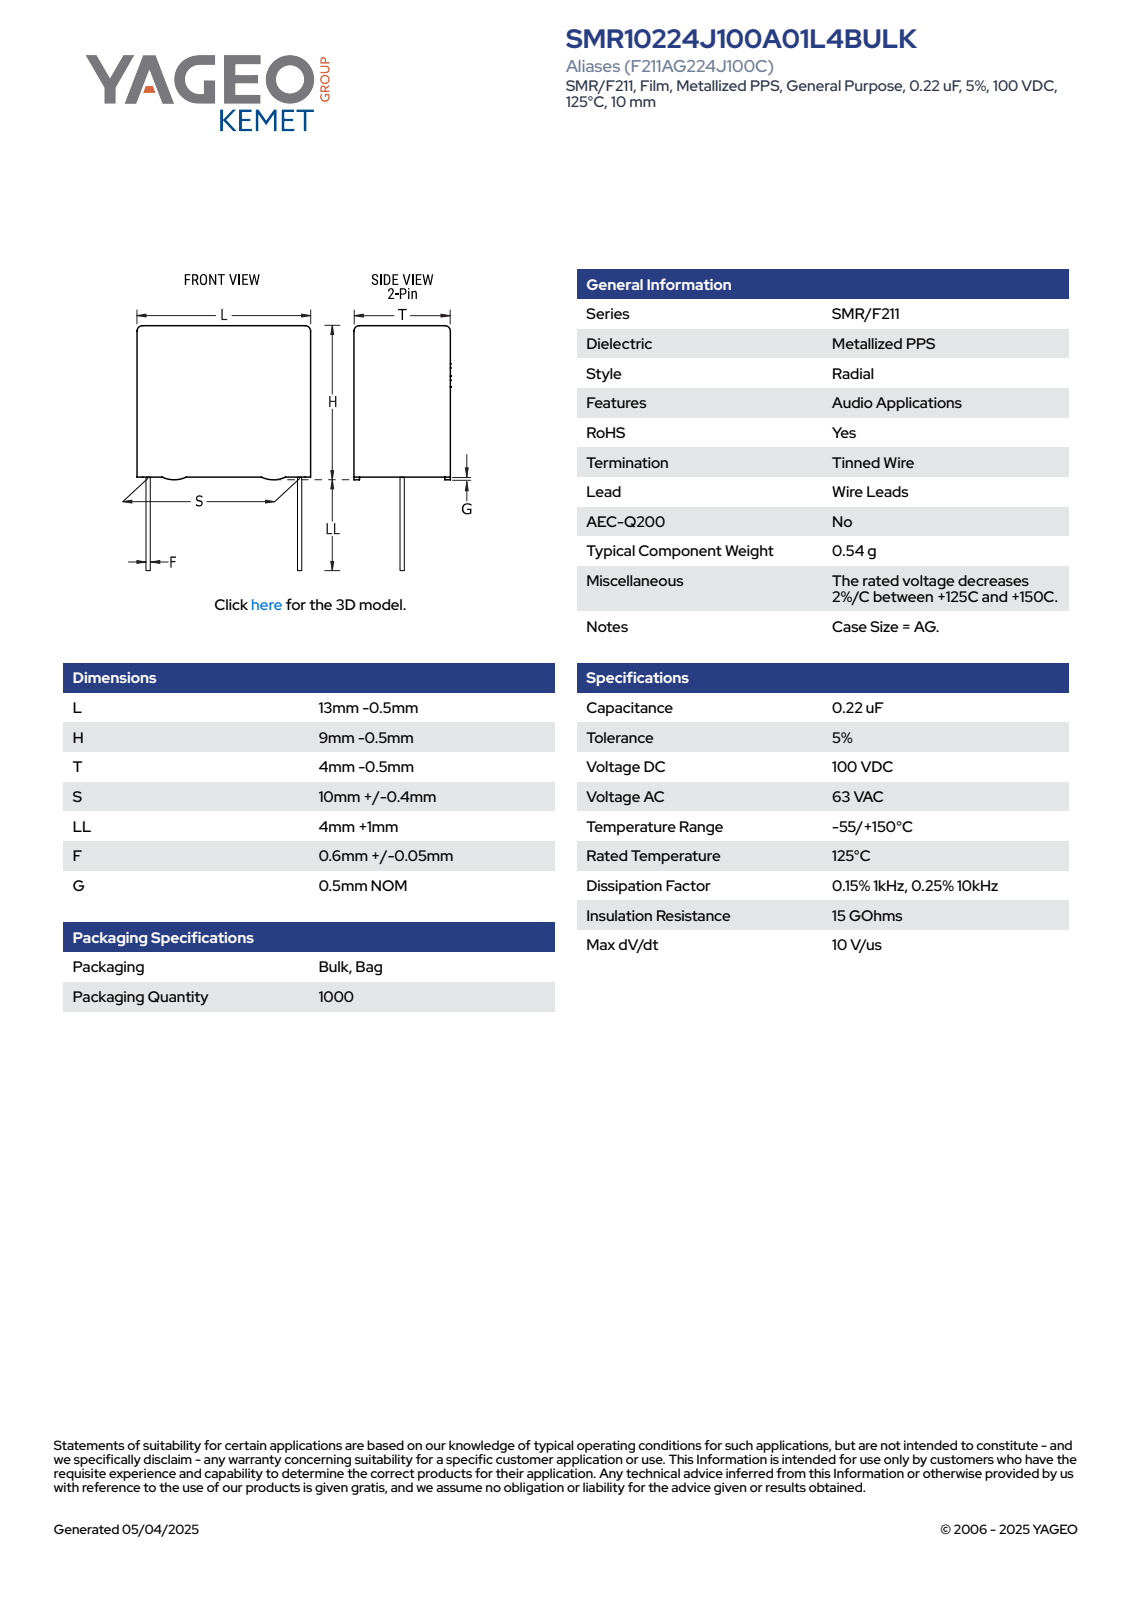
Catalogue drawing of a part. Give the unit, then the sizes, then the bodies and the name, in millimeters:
Units: millimetres
Overall size (bounding box): 13.5 × 12.5 × 3.5
Round bosses / shafts (diameter × count): ⌀0.65 ×2
Partial cylindrical surfaces — rounded edges, fillets, slot ends (radius × count): R0.5 ×4
Main face-to-face distances: 3.5, 8, 12.5, 3.3, 3.1, 0.5, 8.5, 5, 5.5, 13.5
Volume: 353 mm³ · Surface area: 385 mm²
Bodies: 4 solids, 89 faces (81 planar, 8 cylindrical, 0 other)
Part name (STEP PRODUCT): CFR_RBG_13X9X4_L12.5H8.5T3.5S10LL5F0.65G0.5
STEP written by: SolidWorks 2021 (AUTOMOTIVE_DESIGN)
